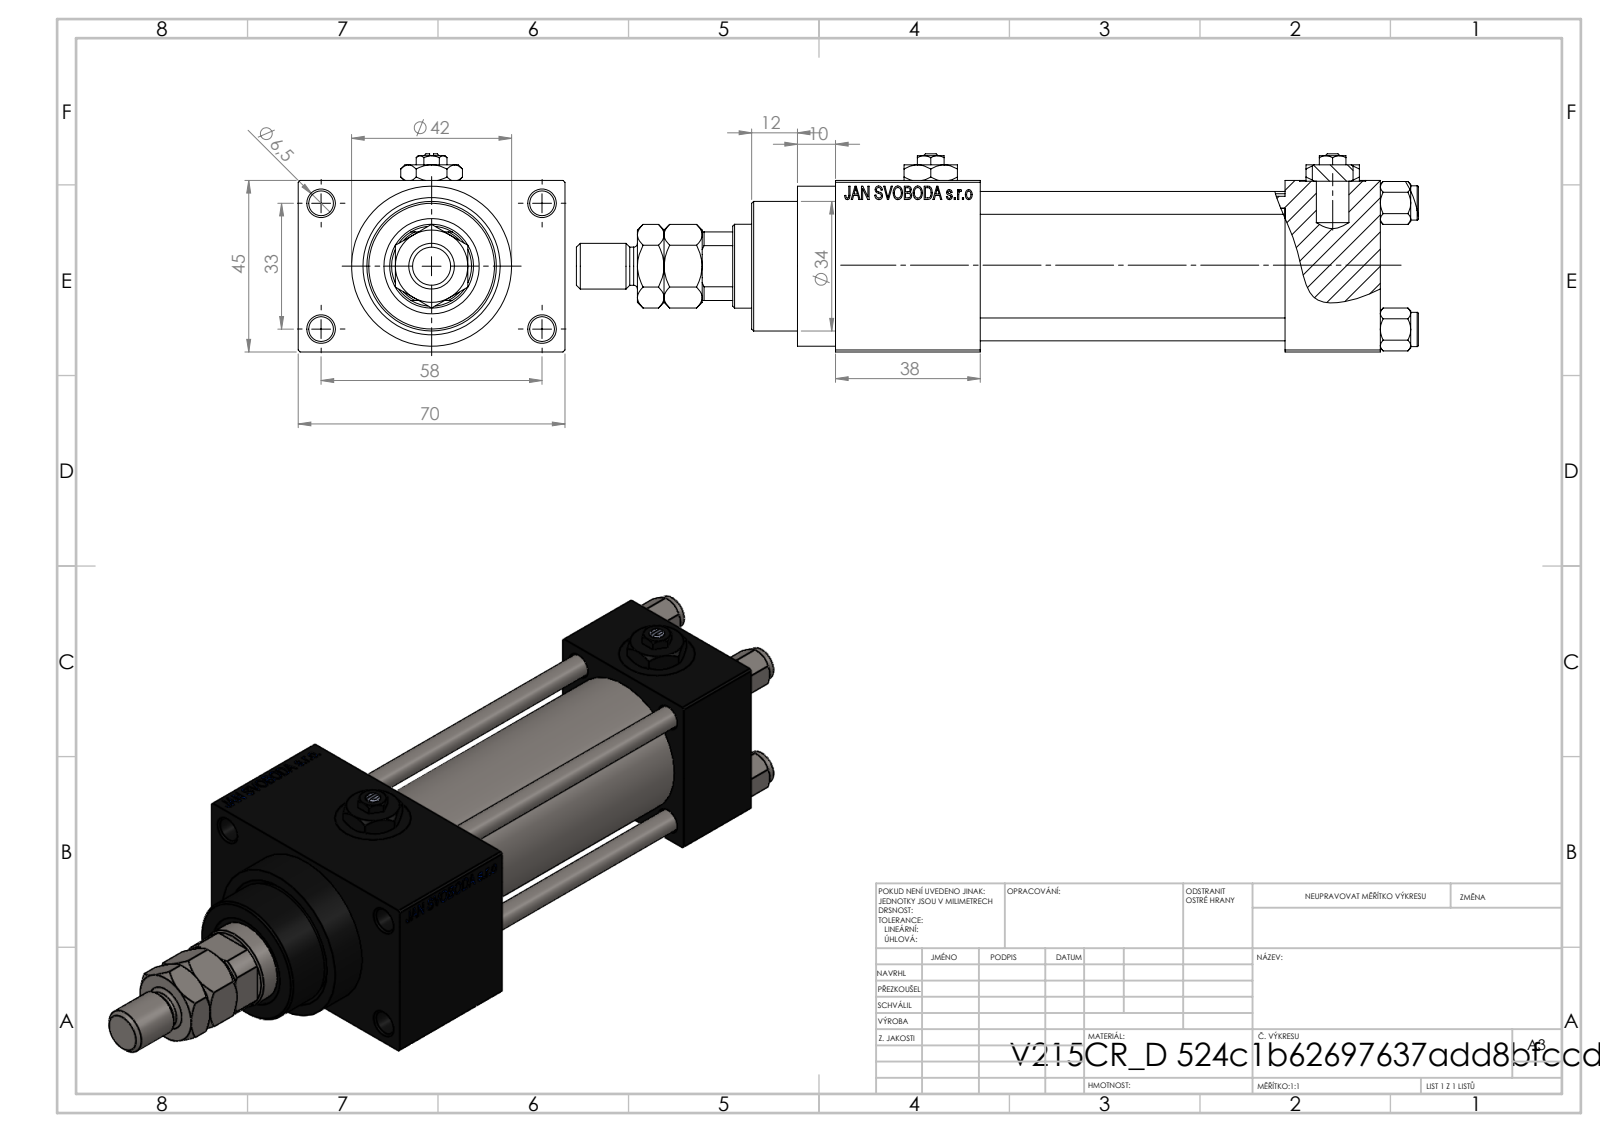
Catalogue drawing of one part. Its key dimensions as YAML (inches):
part_name: "NUT_M5_D; V215CR_D_Body; Zatka_pro_OIL_PORT; V215CR_D_TYCINKA (+3 more)"
step_written_by: "SolidWorks 2019 (CONFIG_CONTROL_DESIGN)"
units: inches
bodies: {solids: 14, faces: 1252, planar: 557, cylindrical: 103, other: 592}
overall_size: [8.701, 2.756, 2.047]
volume: 16.68
surface_area: 147.1
round_holes:
  - {diameter: 0.236, count: 4}
  - {diameter: 0.256, count: 4}
  - {diameter: 0.518, count: 4}
  - {diameter: 0.787, count: 4}
  - {diameter: 0.276, count: 3}
  - {diameter: 0.413, count: 1}
  - {diameter: 0.866, count: 1}
  - {diameter: 0.945, count: 1}
  - {diameter: 0.984, count: 1}
  - {diameter: 1.26, count: 1}
  - {diameter: 1.299, count: 1}
round_bosses_or_shafts:
  - {diameter: 0.354, count: 4}
  - {diameter: 1.654, count: 1}
  - {diameter: 1.496, count: 1}
  - {diameter: 1.339, count: 1}
  - {diameter: 0.472, count: 1}
  - {diameter: 0.394, count: 1}
partial_cylinders:
  - {radius: 0.413, count: 1}
face_to_face_distances: [1.772, 0.984, 0.492, 3.15, 4.134, 2.264, 4.646, 1.496, 5.63, 2.756]
hole_center_spacings: [0.488, 0.924, 1.307, 1.314, 1.392, 1.795, 2.219, 1.299]
